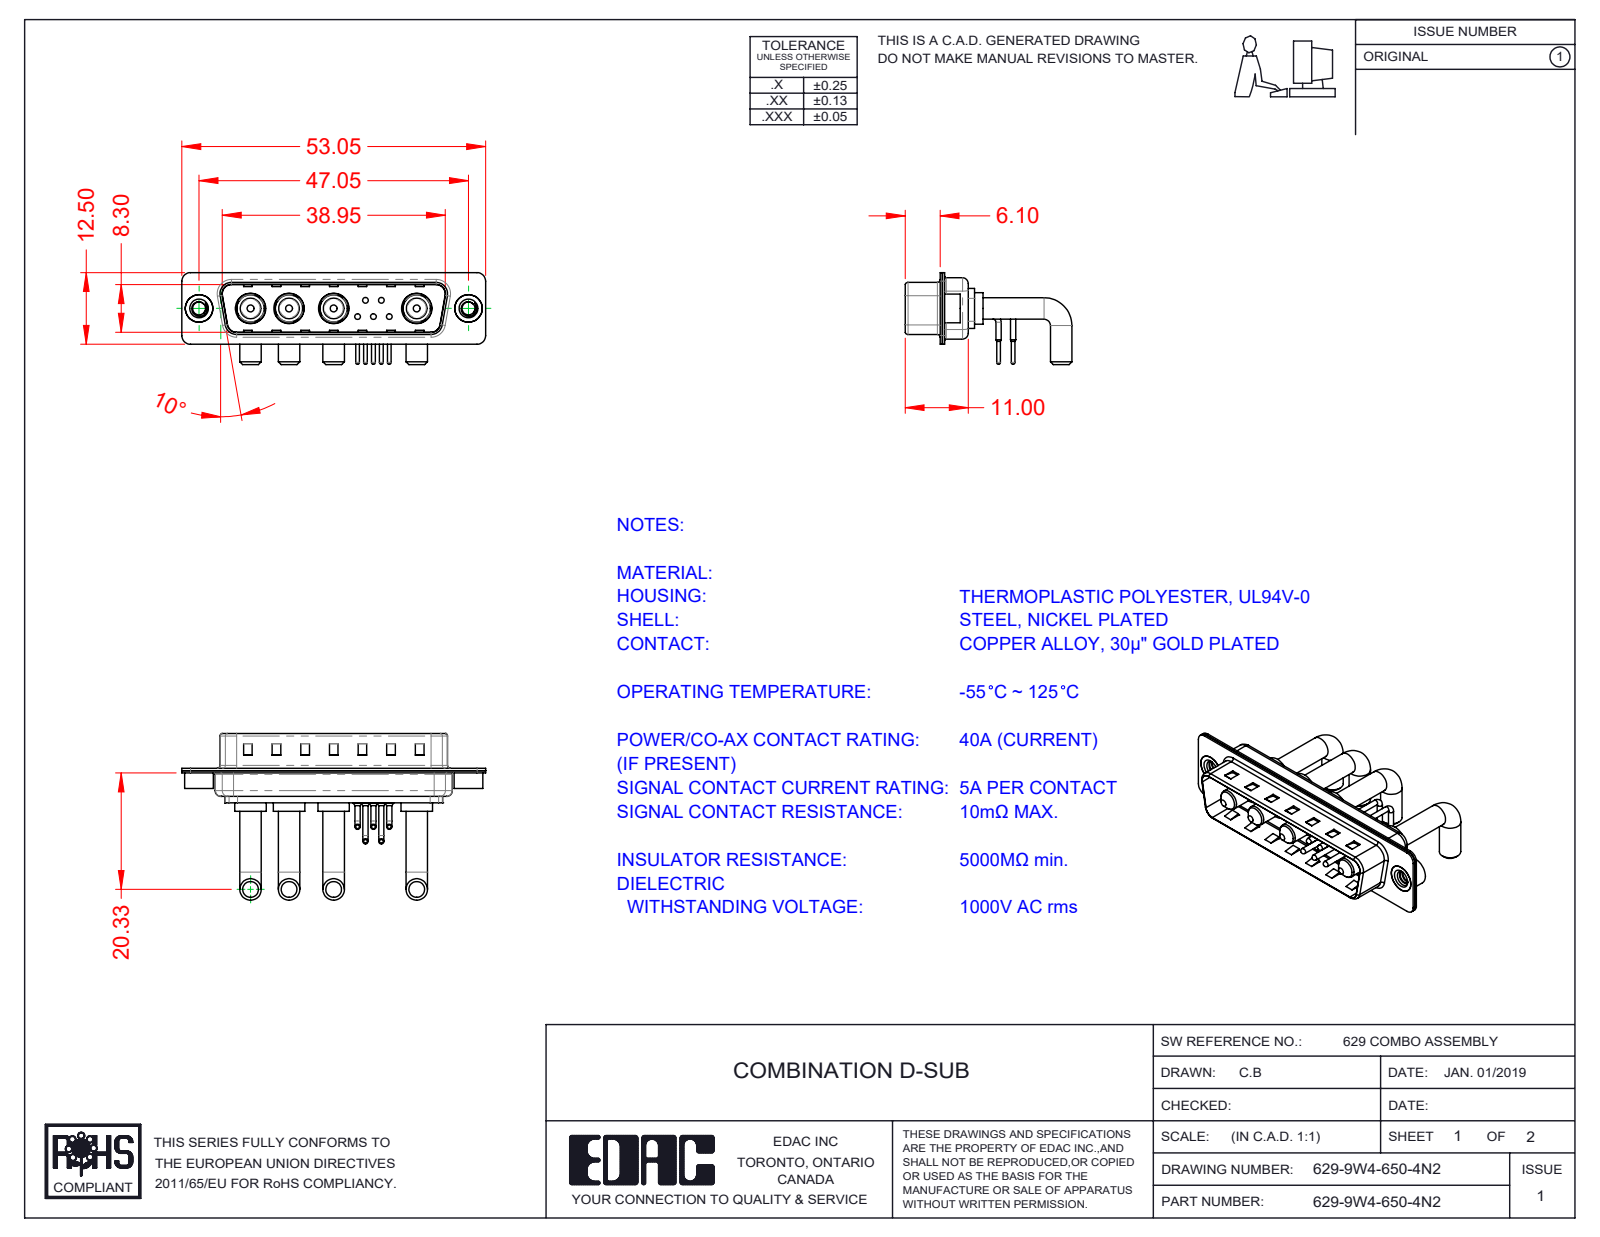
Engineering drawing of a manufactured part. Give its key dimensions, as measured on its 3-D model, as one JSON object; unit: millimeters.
{"part_name": "629Combo Housing_9W4; 629Combo Threaded Rivet_2; 629Combo Shell Rear_25 Contacts; 629-9W4-650-4N2 (+4 more)", "step_written_by": "SolidWorks 2020 (CONFIG_CONTROL_DESIGN)", "units": "millimeters", "bodies": {"solids": 18, "faces": 1098, "planar": 531, "cylindrical": 401, "other": 166}, "overall_size": [53.05, 29.11, 16.05], "volume_mm3": 3912, "surface_area_mm2": 7763, "round_holes": [[0.75, 5], [1.6, 5], [2, 5], [4.85, 4], [5.3, 4], [2.26, 2], [4, 2], [4.8, 2]], "round_bosses_or_shafts": [[0.9, 10], [3.75, 8], [1.5, 5], [1, 5], [0.65, 5], [5.5, 4], [5.2, 4], [4.75, 4]], "partial_cylinders_radius": [[1.5, 16], [2, 12], [0.5, 8], [1.6, 8], [1.01, 5], [0.25, 4], [0.6, 4], [0.65, 4]], "face_to_face_distances": [0.4, 0.8, 9.5, 9.1, 8.7, 9.9, 0.75, 1.2, 5.6, 0.35], "hole_center_spacings": [3.16, 2.77, 5.04, 14.5, 2.78, 4.4, 4.41, 5]}
